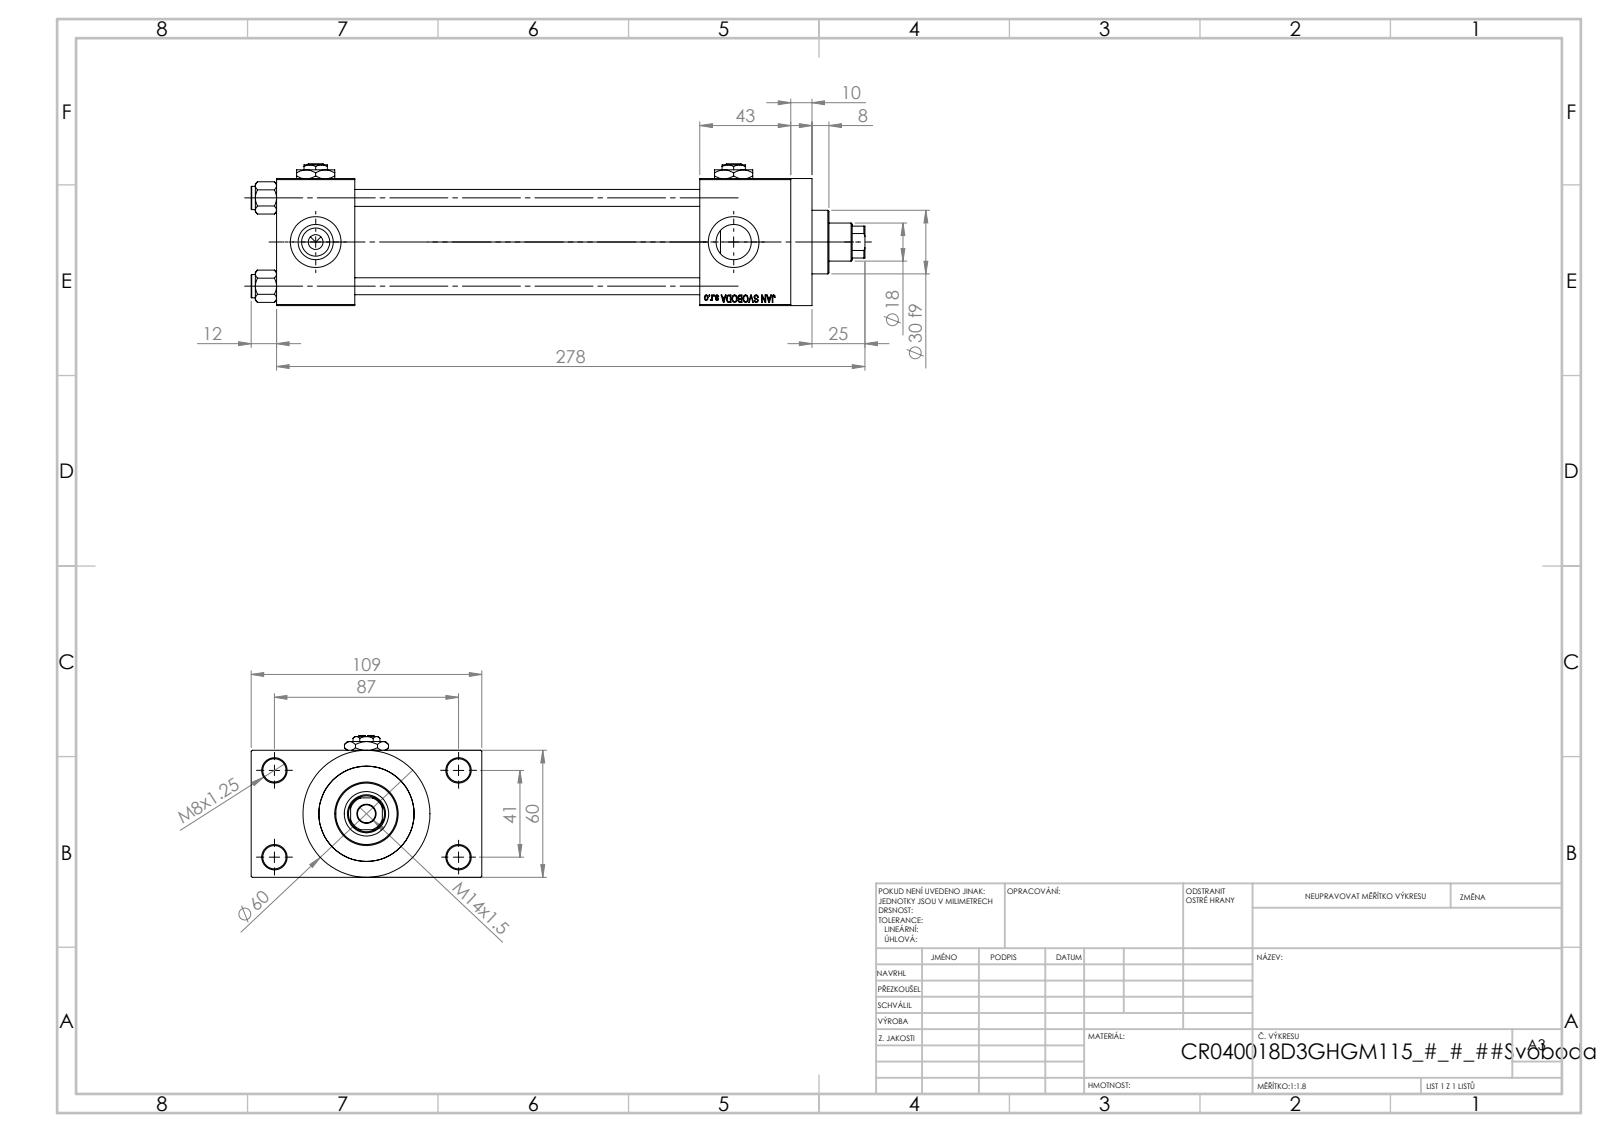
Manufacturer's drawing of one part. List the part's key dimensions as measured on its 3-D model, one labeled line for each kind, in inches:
Part name (STEP PRODUCT): V215_VC_A; V215CR_D_Body; V215CR_D_TYCINKA; Zatka_pro_OIL_PORT (+2 more)
STEP written by: SolidWorks 2019 (CONFIG_CONTROL_DESIGN)
Units: inches
Bodies: 13 solids, 1205 faces (546 planar, 99 cylindrical, 560 other)
Overall size (bounding box): 11.417 × 4.291 × 2.638
Volume: 36.66 in³ · Surface area: 263.6 in²
Round holes (diameter × count): ⌀0.315 ×4, ⌀0.433 ×4, ⌀0.656 ×4, ⌀0.945 ×4, ⌀0.276 ×3, ⌀0.335 ×1, ⌀0.709 ×1, ⌀0.827 ×1, ⌀1.22 ×1, ⌀1.575 ×1, ⌀1.772 ×1
Round bosses / shafts (diameter × count): ⌀0.433 ×4, ⌀2.362 ×1, ⌀1.811 ×1, ⌀1.181 ×1
Partial cylindrical surfaces — rounded edges, fillets, slot ends (radius × count): R0.335 ×1
Main face-to-face distances: 2.362, 6.417, 0.965, 3.327, 1.457, 7.874, 1.693, 9.567, 8.11, 0.394
Hole centre spacings: 0.892, 1.161, 1.642, 1.856, 1.893, 2.533, 3.011, 1.614
